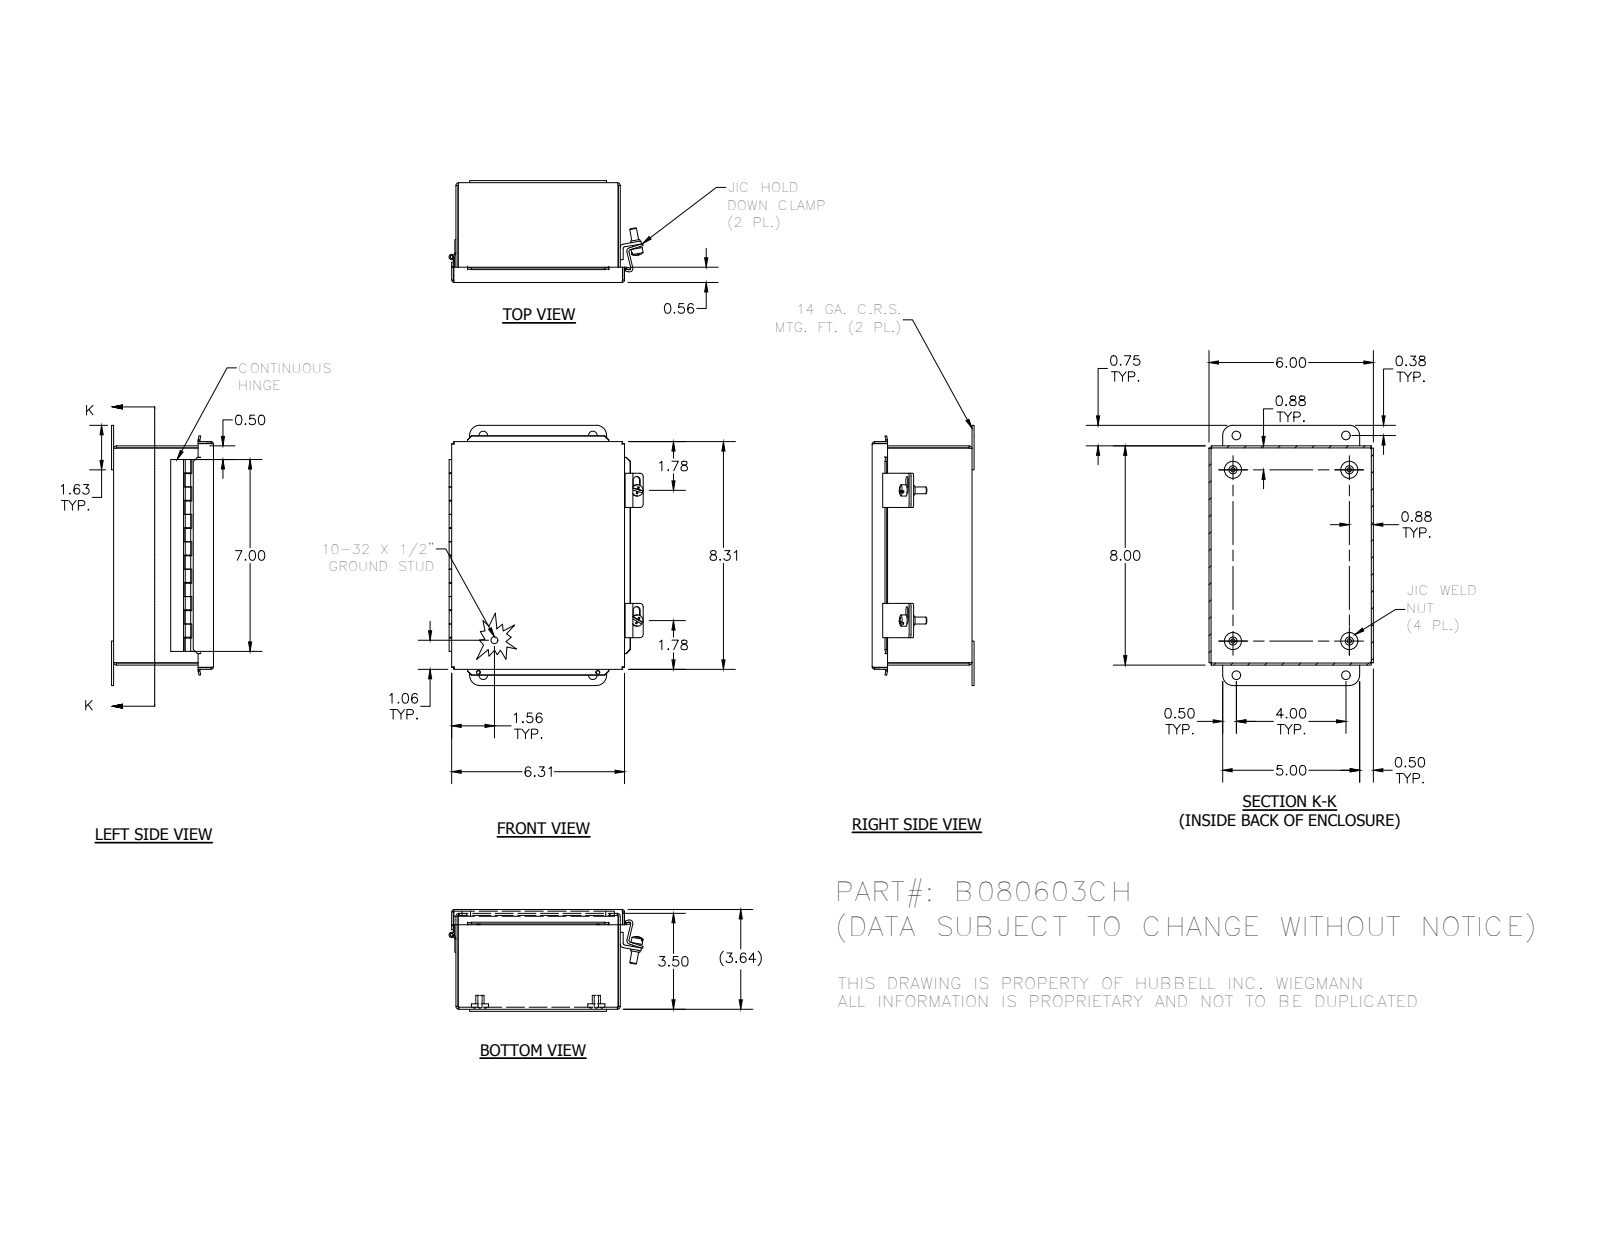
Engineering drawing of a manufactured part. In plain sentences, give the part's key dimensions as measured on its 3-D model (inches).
The part is named "B080603CH; 3499; 3482; C1001 (+8 more)". Its 3-D file was written by "Autodesk Inventor 2012 (AUTOMOTIVE_DESIGN)". It is 20 solids with 459 faces: 299 planar, 115 cylindrical and 45 other. Overall it measures 9.5 by 7.087 by 3.719 inches. Its volume is 21.1 cubic inches and its surface area 572.6 square inches. Round holes: 4 of diameter 0.156, 4 of diameter 0.31, 2 of diameter 0.14, 2 of diameter 0.196, 1 of diameter 0.116. Round bosses or shafts: 4 of diameter 0.625, 4 of diameter 0.3, 3 of diameter 0.25, 2 of diameter 0.41, 2 of diameter 0.344, 1 of diameter 0.2, 1 of diameter 0.19, 1 of diameter 0.1. Partial cylindrical surfaces (rounded edges, fillets, slot ends): 15 of radius 0.031, 8 of radius 0.105, 8 of radius 0.125, 7 of radius 0.093, 4 of radius 0.133, 4 of radius 0.375, 3 of radius 0.063, 3 of radius 0.126. The main face-to-face distances are 0.074, 3.583, 5.926, 3.644, 0.062, 3.509, 3.57, 7.926, 6, 5.852. The hole center spacings are 4.31, 1.256, 1.257, 4, 4.25, 7.501, 7.502, 7.558.
